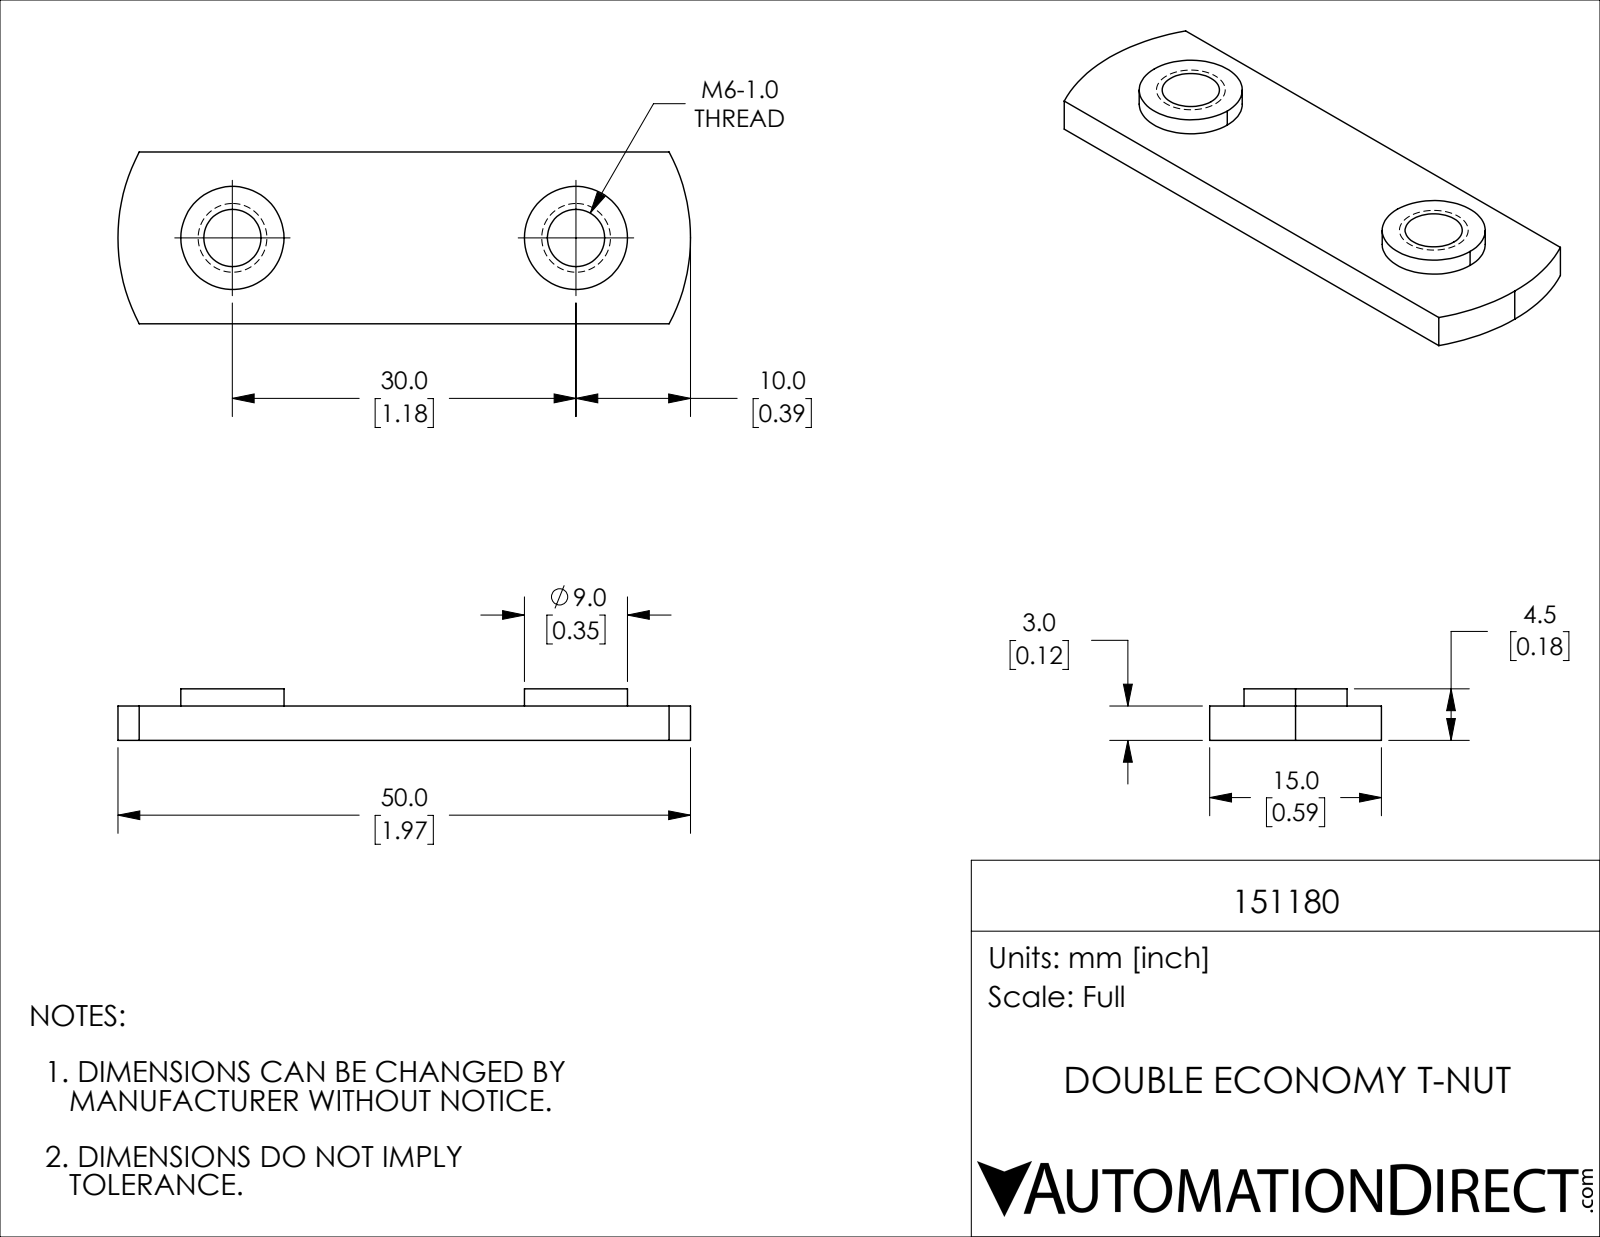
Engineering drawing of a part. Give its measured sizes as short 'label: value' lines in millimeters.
name: 151180
written by: SolidWorks 2021 (CONFIG_CONTROL_DESIGN)
unit: mm
bodies: 1 solid, 17 faces (6 planar, 11 cylindrical, 0 other)
size: 50 × 15 × 4.5
volume: 2 210 mm³; area: 1 983 mm²
holes: 2× ⌀5
bosses: 2× ⌀9
rounds: 2× R16
face distances: 3, 15, 1.5, 4.5
hole spacings: 30
